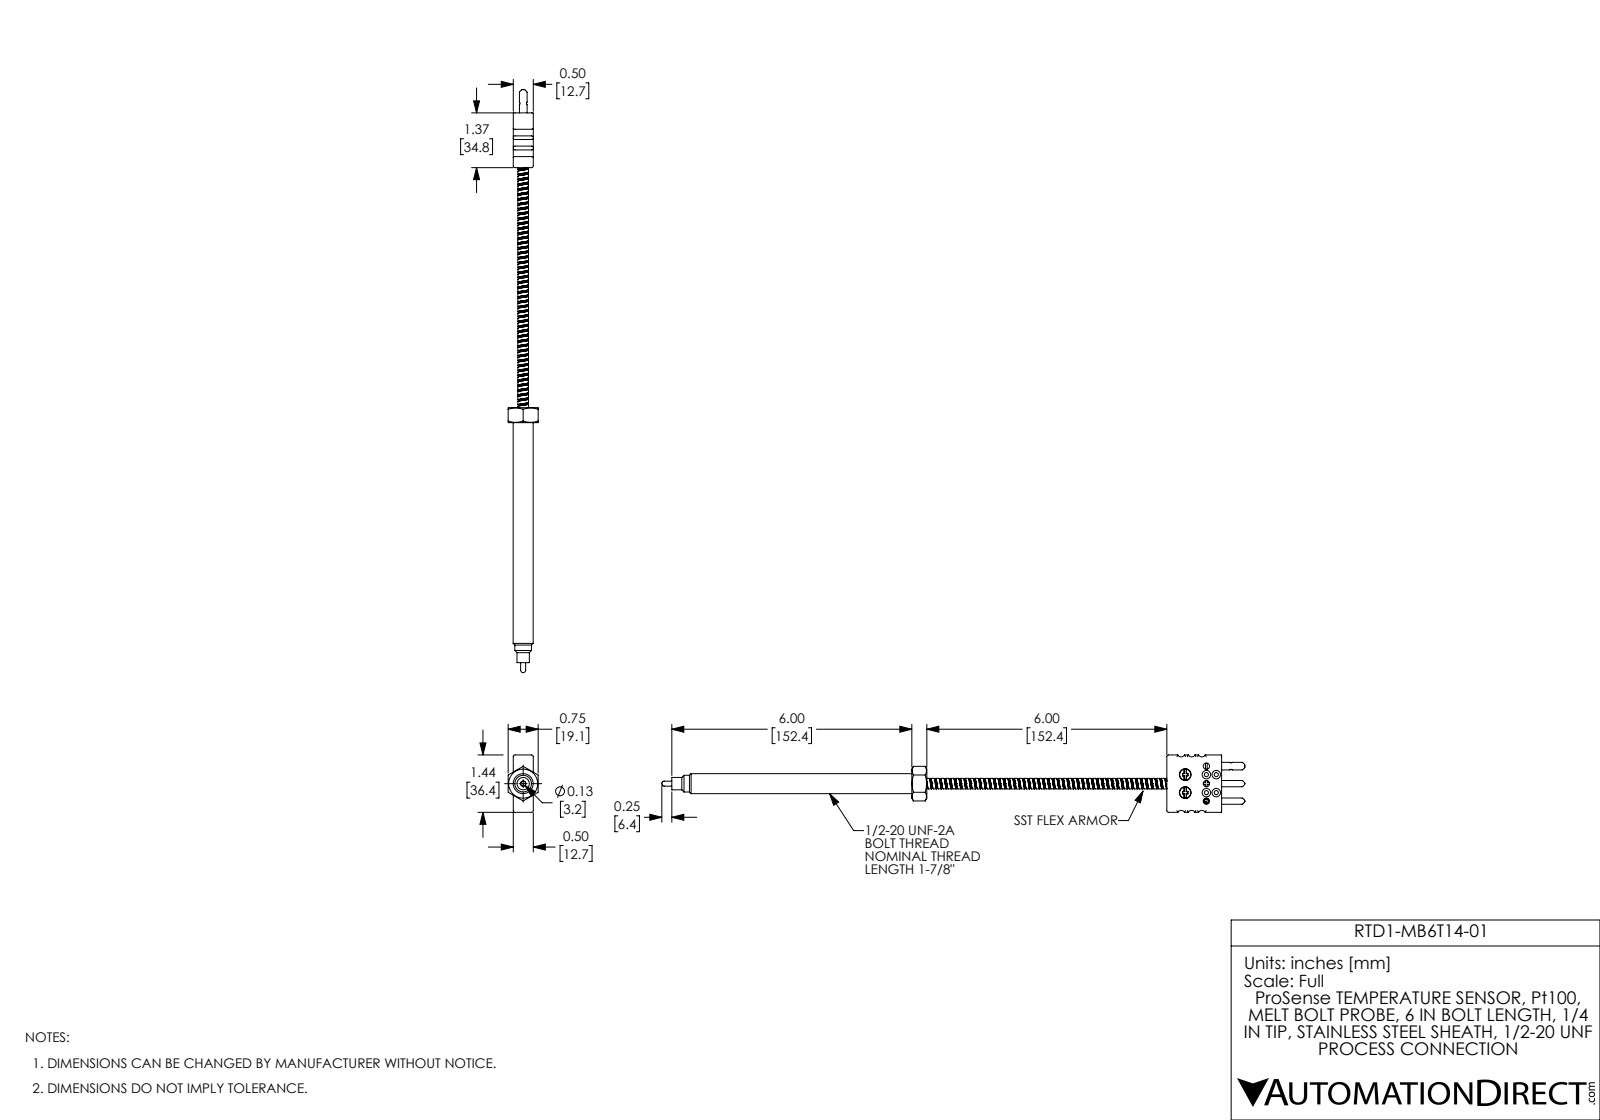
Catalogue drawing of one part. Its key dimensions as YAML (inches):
part_name: "RTD1-MB6T14-01"
step_written_by: "SolidWorks 2017 (AUTOMOTIVE_DESIGN)"
units: inches
bodies: {solids: 3, faces: 412, planar: 106, cylindrical: 190, other: 116}
overall_size: [14.576, 1.435, 0.75]
volume: 2.57
surface_area: 26.56
round_holes:
  - {diameter: 0.103, count: 4}
  - {diameter: 0.158, count: 3}
  - {diameter: 0.185, count: 2}
  - {diameter: 0.294, count: 2}
  - {diameter: 0.135, count: 1}
  - {diameter: 0.308, count: 1}
round_bosses_or_shafts:
  - {diameter: 0.278, count: 2}
  - {diameter: 0.156, count: 2}
  - {diameter: 0.102, count: 2}
  - {diameter: 0.5, count: 1}
  - {diameter: 0.417, count: 1}
  - {diameter: 0.309, count: 1}
  - {diameter: 0.265, count: 1}
  - {diameter: 0.191, count: 1}
partial_cylinders:
  - {radius: 0.045, count: 8}
  - {radius: 0.095, count: 6}
  - {radius: 0.01, count: 4}
face_to_face_distances: [0.5, 6, 1.369, 0.75, 7.369, 1.435, 6.375, 7.744, 0.375, 0.622]
hole_center_spacings: [0.529, 0.57, 0.776, 0.212, 0.225, 0.247, 0.326, 0.334]
